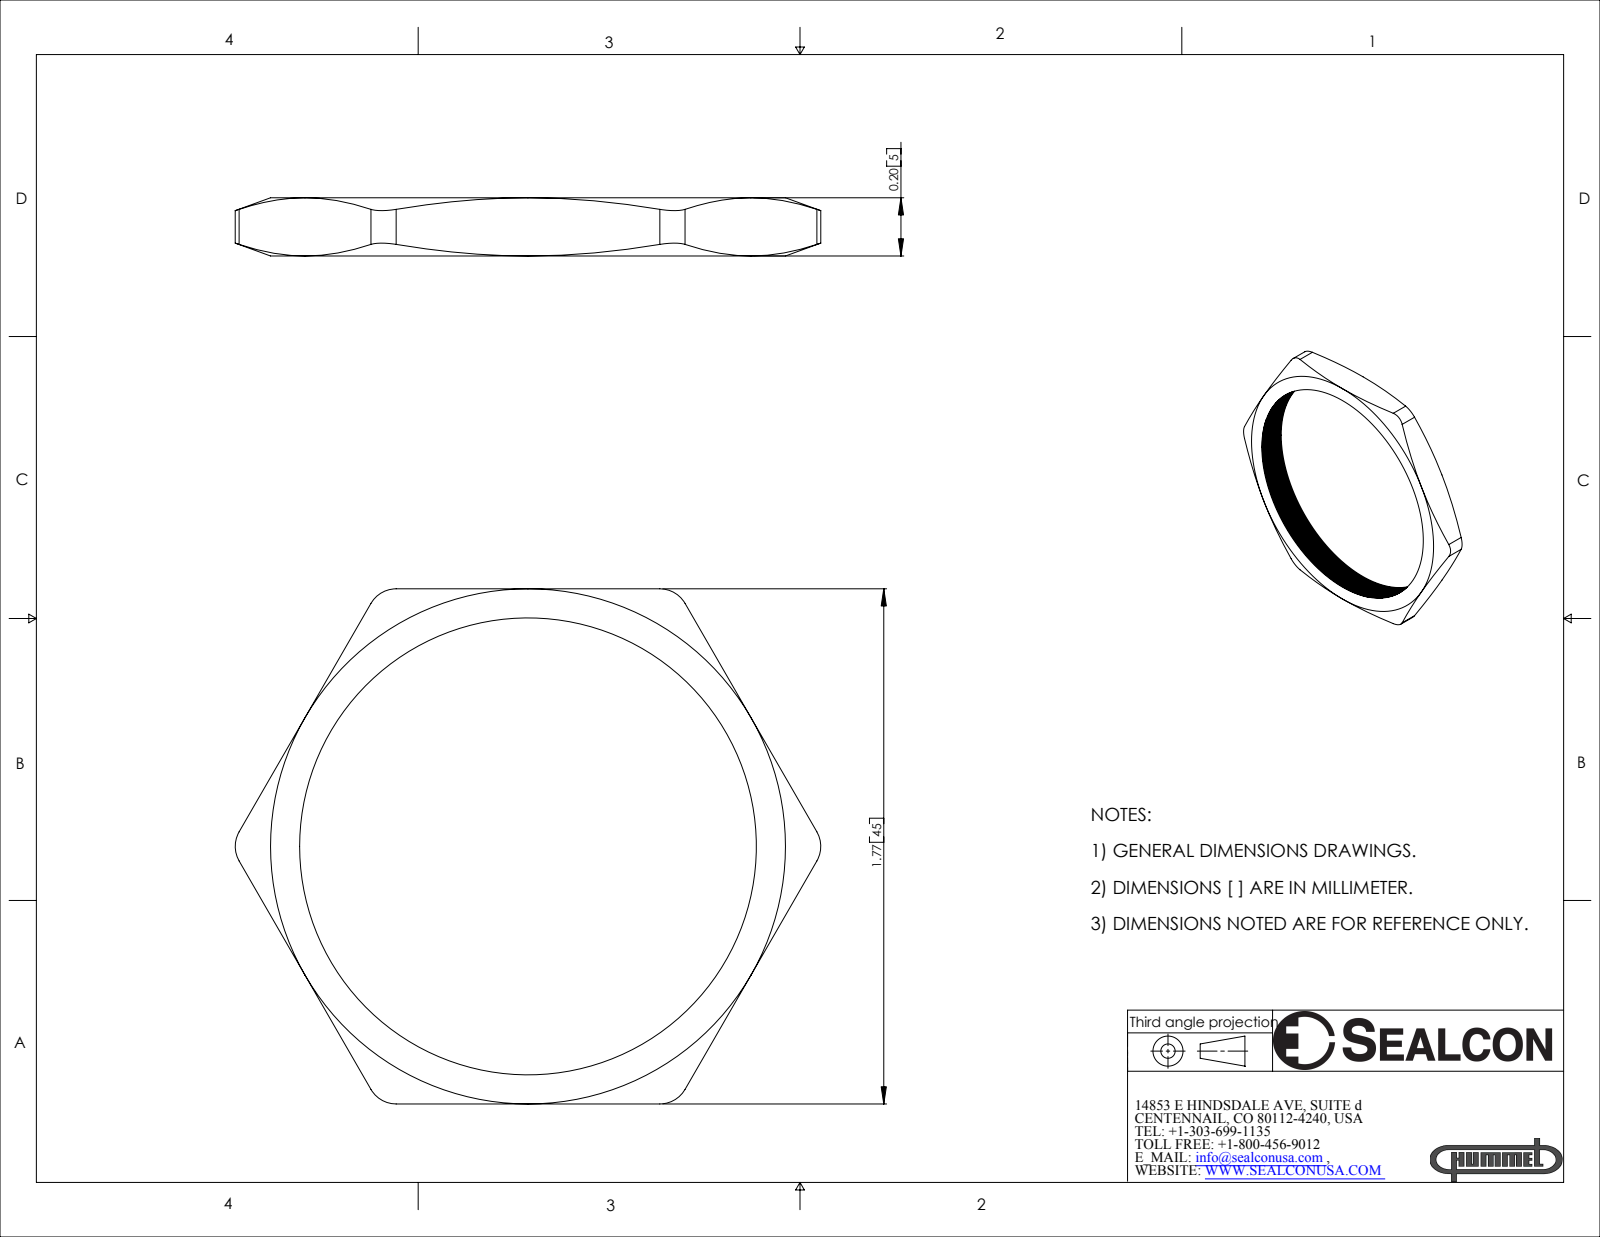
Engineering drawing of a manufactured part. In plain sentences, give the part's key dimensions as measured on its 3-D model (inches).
The part is named "NM-40-BR". Its 3-D file was written by "SolidWorks 2007 (CONFIG_CONTROL_DESIGN)". It is 1 solid with 127 faces: 8 planar, 7 cylindrical and 112 other. Overall it measures 2.013 by 1.77 by 0.2 inches. Its volume is 0.136 cubic inches and its surface area 4.525 square inches. Partial cylindrical surfaces (rounded edges, fillets, slot ends): 6 of radius 0.1. The main face-to-face distances are 1.77, 0.2.
